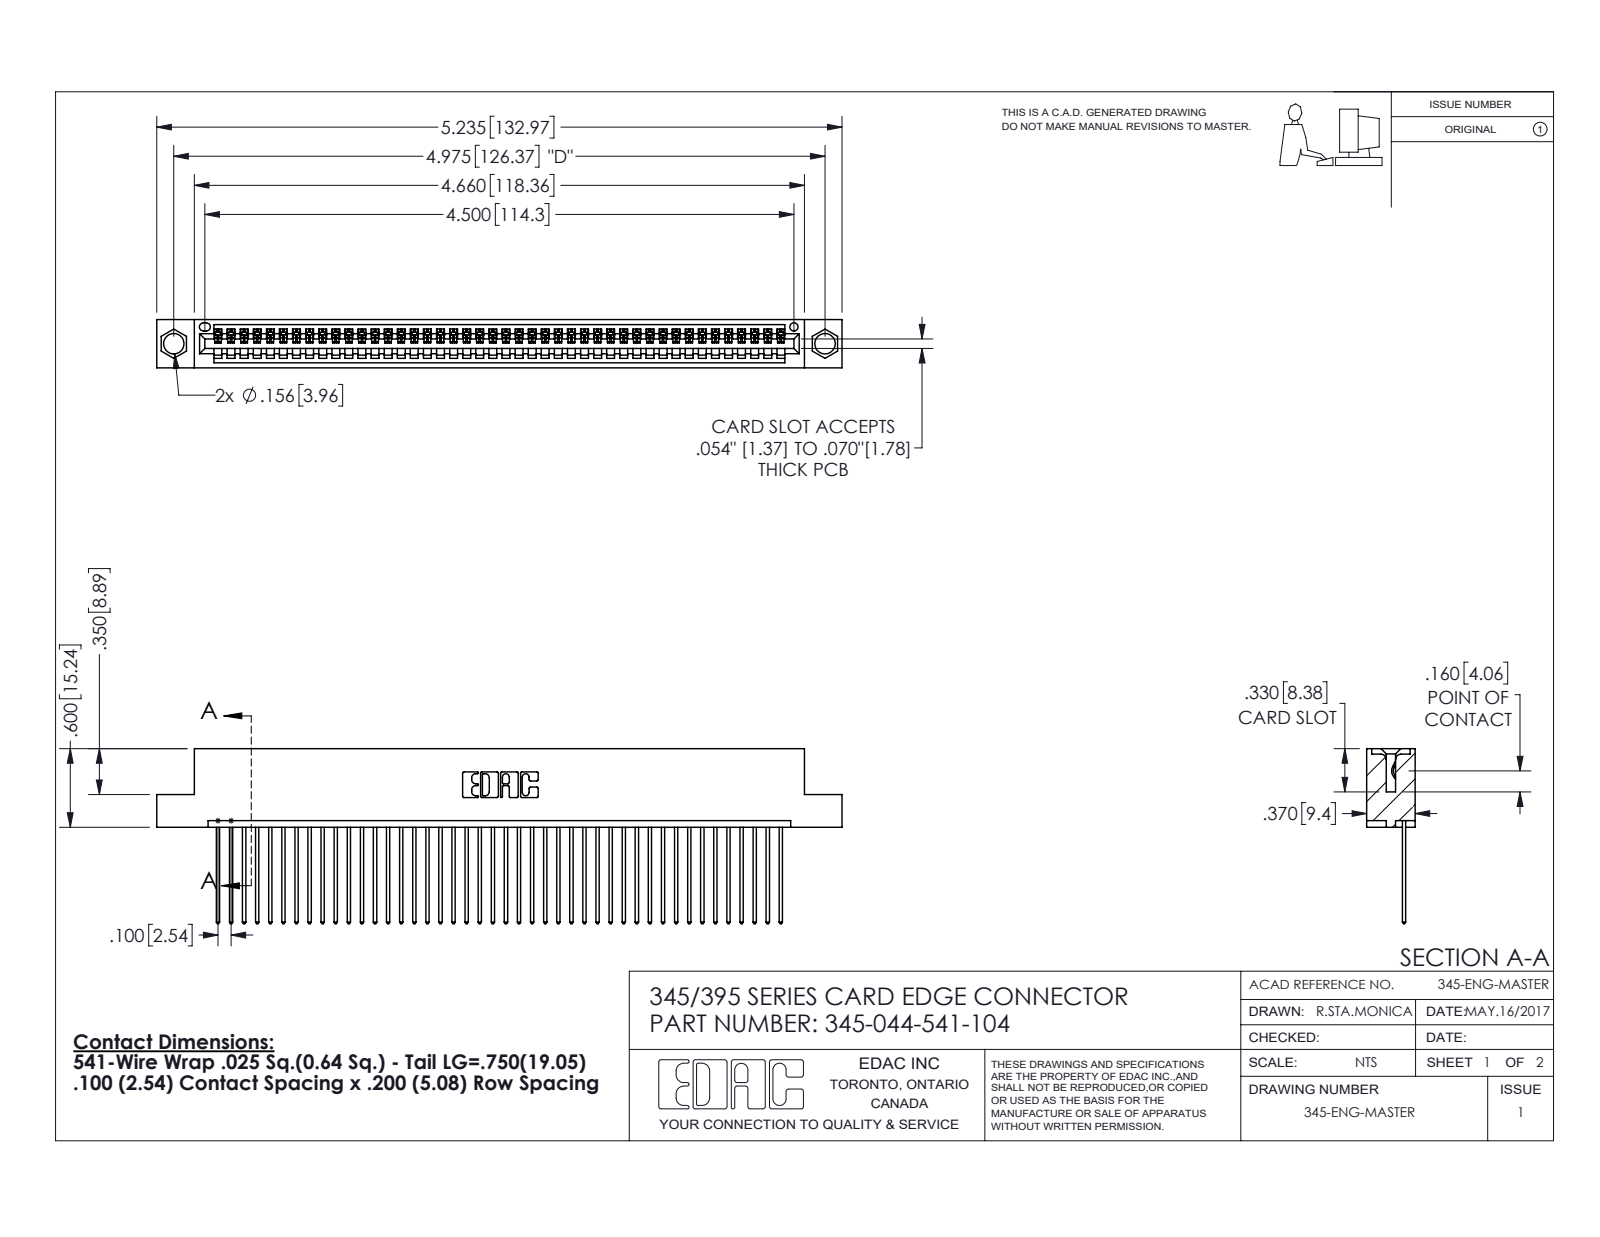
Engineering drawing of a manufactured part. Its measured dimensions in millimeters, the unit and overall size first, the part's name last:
Units: millimetres
Overall size (bounding box): 133 × 34 × 9.4
Round holes (diameter × count): ⌀4 ×2, ⌀1.6 ×1
Partial cylindrical surfaces — rounded edges, fillets, slot ends (radius × count): R0.2 ×88, R0.3 ×88, R0.3 ×22, R0.2 ×6, R0.8 ×6, R0.7 ×3, R0.8 ×2, R1 ×2
Main face-to-face distances: 1.8, 7.6, 2.5, 6.9, 0.6, 9.4, 5.1, 5.7, 3.8, 1.8
Hole centre spacings: 6.9, 120.4, 126.4
Volume: 12 700 mm³ · Surface area: 17 580 mm²
Bodies: 45 solids, 2692 faces (1854 planar, 838 cylindrical, 0 other)
Part name (STEP PRODUCT): 345-292-001_345-293-141; 345-044-541-104; 345 Part_Flush Mounting Lugs - 0.156 Dia-TI
STEP written by: SolidWorks 2020 (CONFIG_CONTROL_DESIGN)
